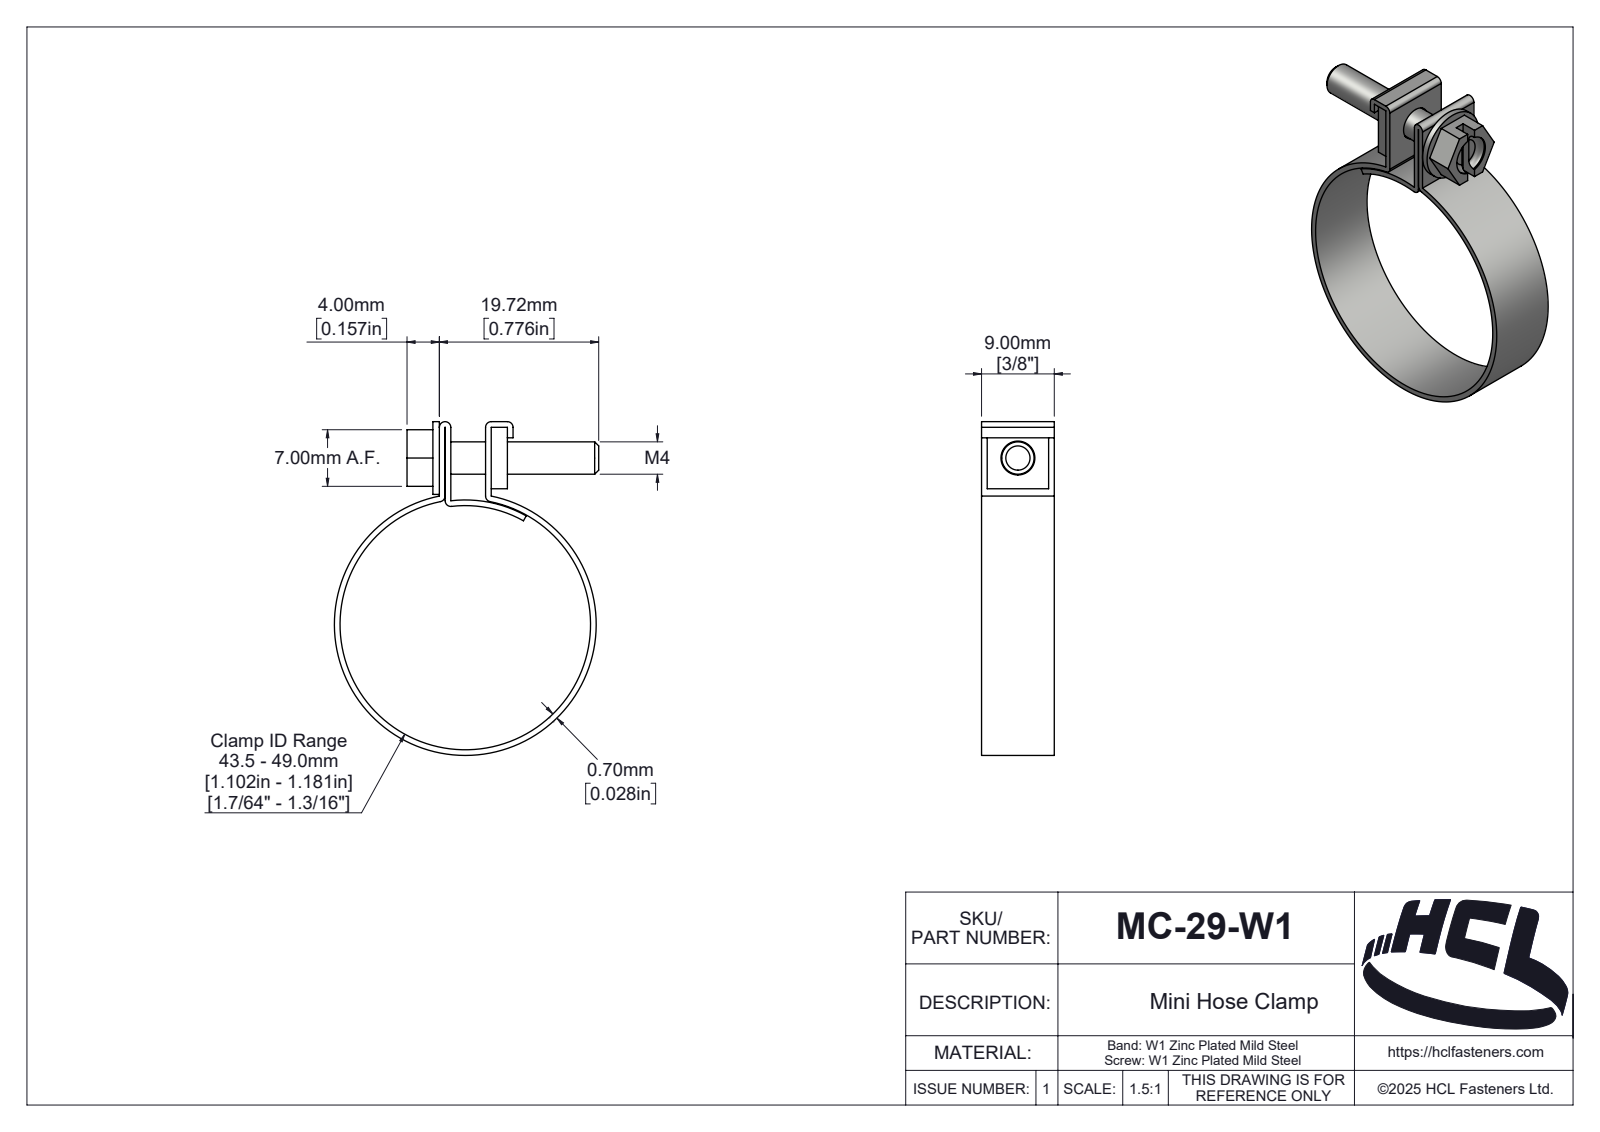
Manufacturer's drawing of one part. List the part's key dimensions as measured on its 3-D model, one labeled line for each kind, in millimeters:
Part name (STEP PRODUCT): MC-29-W1
STEP written by: SolidWorks 2025 (AUTOMOTIVE_DESIGN)
Units: millimetres
Bodies: 3 solids, 170 faces (38 planar, 79 cylindrical, 53 other)
Overall size (bounding box): 41.28 × 32.71 × 9
Volume: 1 318 mm³ · Surface area: 3 266 mm²
Round holes (diameter × count): ⌀4.2 ×1, ⌀5 ×1, ⌀31 ×1
Round bosses / shafts (diameter × count): ⌀32.4 ×1, ⌀9 ×1, ⌀4 ×1
Partial cylindrical surfaces — rounded edges, fillets, slot ends (radius × count): R0.7 ×5, R0.2 ×1, R0.71 ×1, R0.81 ×1, R1.01 ×1, R1.06 ×1, R1.28 ×1, R1.81 ×1
Main face-to-face distances: 0.7, 5, 0.72, 5.72, 6.42, 9, 7, 2, 2.7, 8.42
